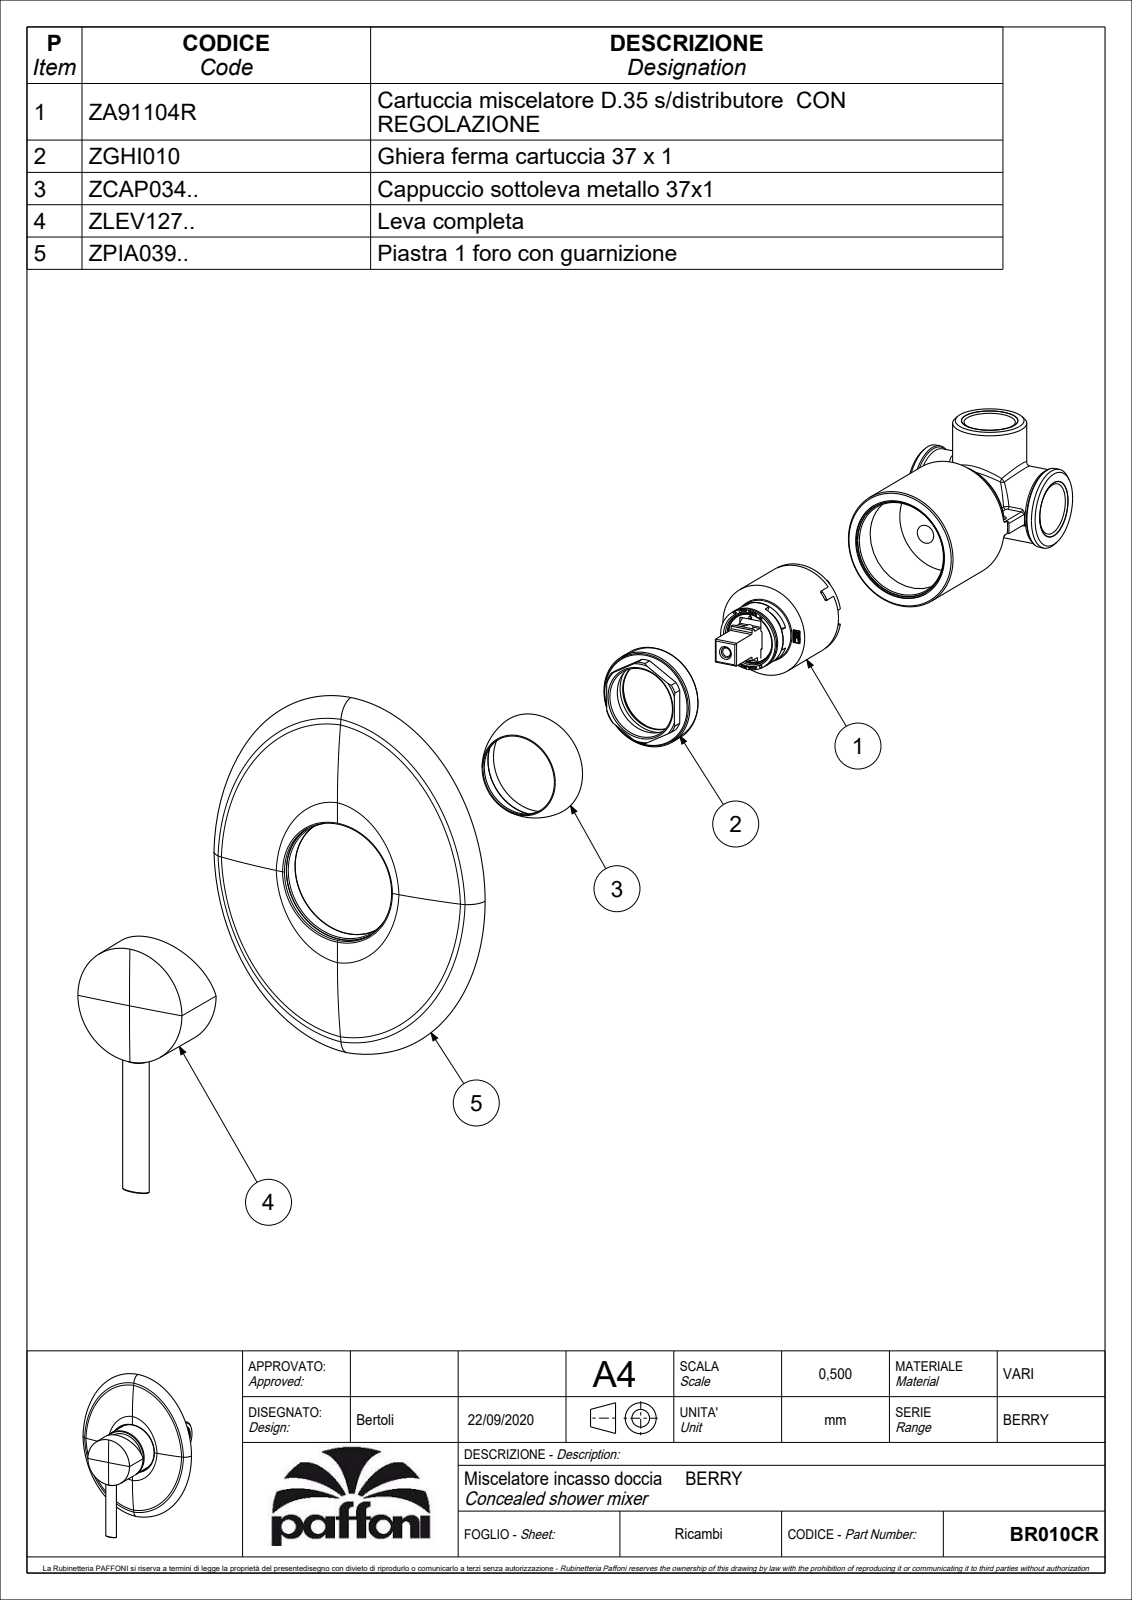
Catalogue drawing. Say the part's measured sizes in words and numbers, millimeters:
The part is named "BR010CR". Its 3-D file was written by "CREO PARAMETRIC BY PTC INC, 2020044 (CONFIG_CONTROL_DESIGN)". It is 2 solids with 992 faces: 583 planar, 229 cylindrical and 180 other. Overall it measures 144.5 by 115 by 59.3 millimeters. Its volume is 80 366 cubic millimeters and its surface area 64 927 square millimeters. Round holes: 3 of diameter 5, 2 of diameter 2, 2 of diameter 4, 2 of diameter 7, 1 of diameter 3, 1 of diameter 3.3, 1 of diameter 3.5, 1 of diameter 7.8, 1 of diameter 8, 1 of diameter 19.5, 1 of diameter 19.9, 1 of diameter 26.8. Round bosses or shafts: 2 of diameter 4.8, 1 of diameter 51, 1 of diameter 49, 1 of diameter 44.8, 1 of diameter 35, 1 of diameter 34.8, 1 of diameter 32.2, 1 of diameter 23.5. Partial cylindrical surfaces (rounded edges, fillets, slot ends): 27 of radius 0.5, 11 of radius 0.15, 4 of radius 0.3, 4 of radius 1, 4 of radius 1.25, 2 of radius 0.8, 1 of radius 1.9, 1 of radius 2.5. The main face-to-face distances are 57, 6.3, 0.5, 1.5, 50.7, 9, 27, 20.7, 30, 9.1. The hole center spacings are 8.6, 10.42, 12, 13.45, 15.13, 21.93, 0.5, 4.75.
